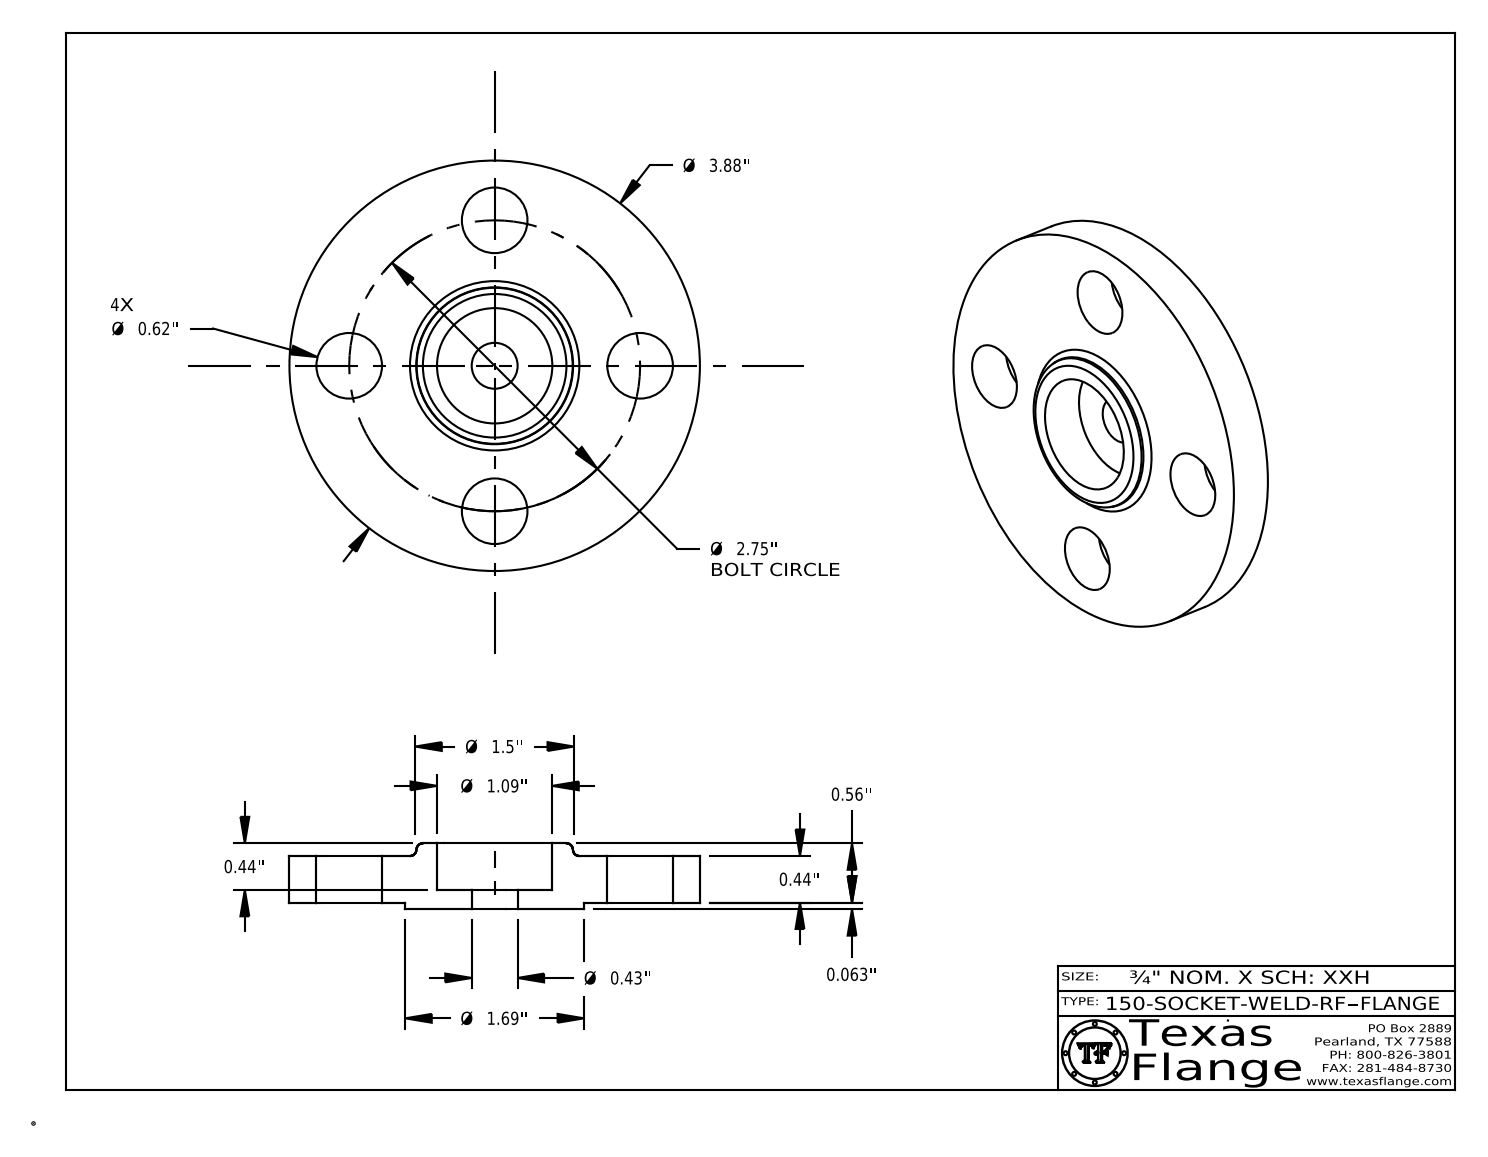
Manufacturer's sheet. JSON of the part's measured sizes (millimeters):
{"part_name": "150-SOCKET-WELD-RF", "step_written_by": "CATIA V5 STEP AP214 (AUTOMOTIVE_DESIGN)", "units": "millimeters", "bodies": {"solids": 1, "faces": 412, "planar": 370, "cylindrical": 36, "other": 6}, "overall_size": [98.6, 98.6, 15.8], "volume_mm3": 75040, "surface_area_mm2": 20790, "round_holes": [[15.7, 4], [11, 1], [12.6, 1], [27.7, 1]], "round_bosses_or_shafts": [[0.8, 8], [98.6, 1], [42.9, 1], [9.9, 1]], "face_to_face_distances": [11.2, 1.6, 12.8, 4.6, 3, 8.1, 15.8, 14.2, 11.2, 3], "hole_center_spacings": [34.9, 49.4, 26.7, 64.5, 69.9]}
